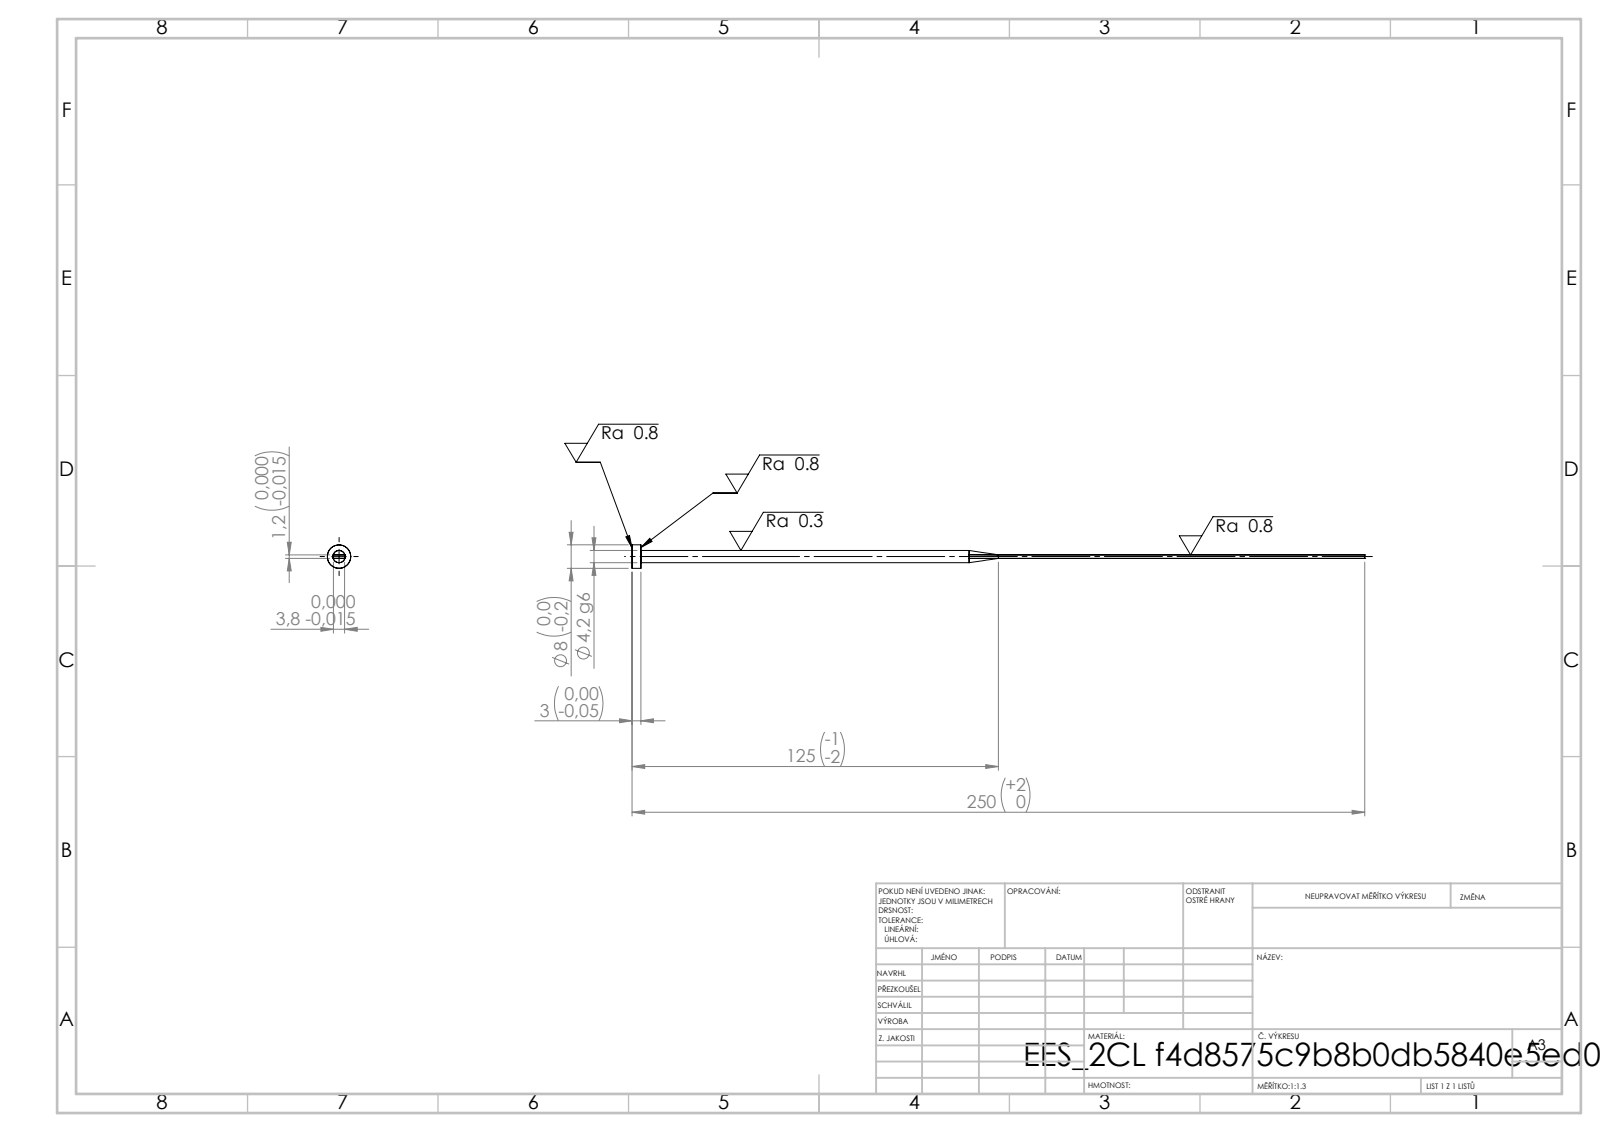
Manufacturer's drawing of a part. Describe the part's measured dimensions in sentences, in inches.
Its 3-D file was written by "SolidWorks 2019 (CONFIG_CONTROL_DESIGN)". It is 1 solid with 15 faces: 7 planar, 4 cylindrical and 4 other. Overall it measures 9.843 by 0.315 by 0.315 inches. Its volume is 0.144 cubic inches and its surface area 4.661 square inches. Round bosses or shafts: 1 of diameter 0.315, 1 of diameter 0.165. The main face-to-face distances are 0.047, 0.15, 0.118, 9.843, 9.724.
